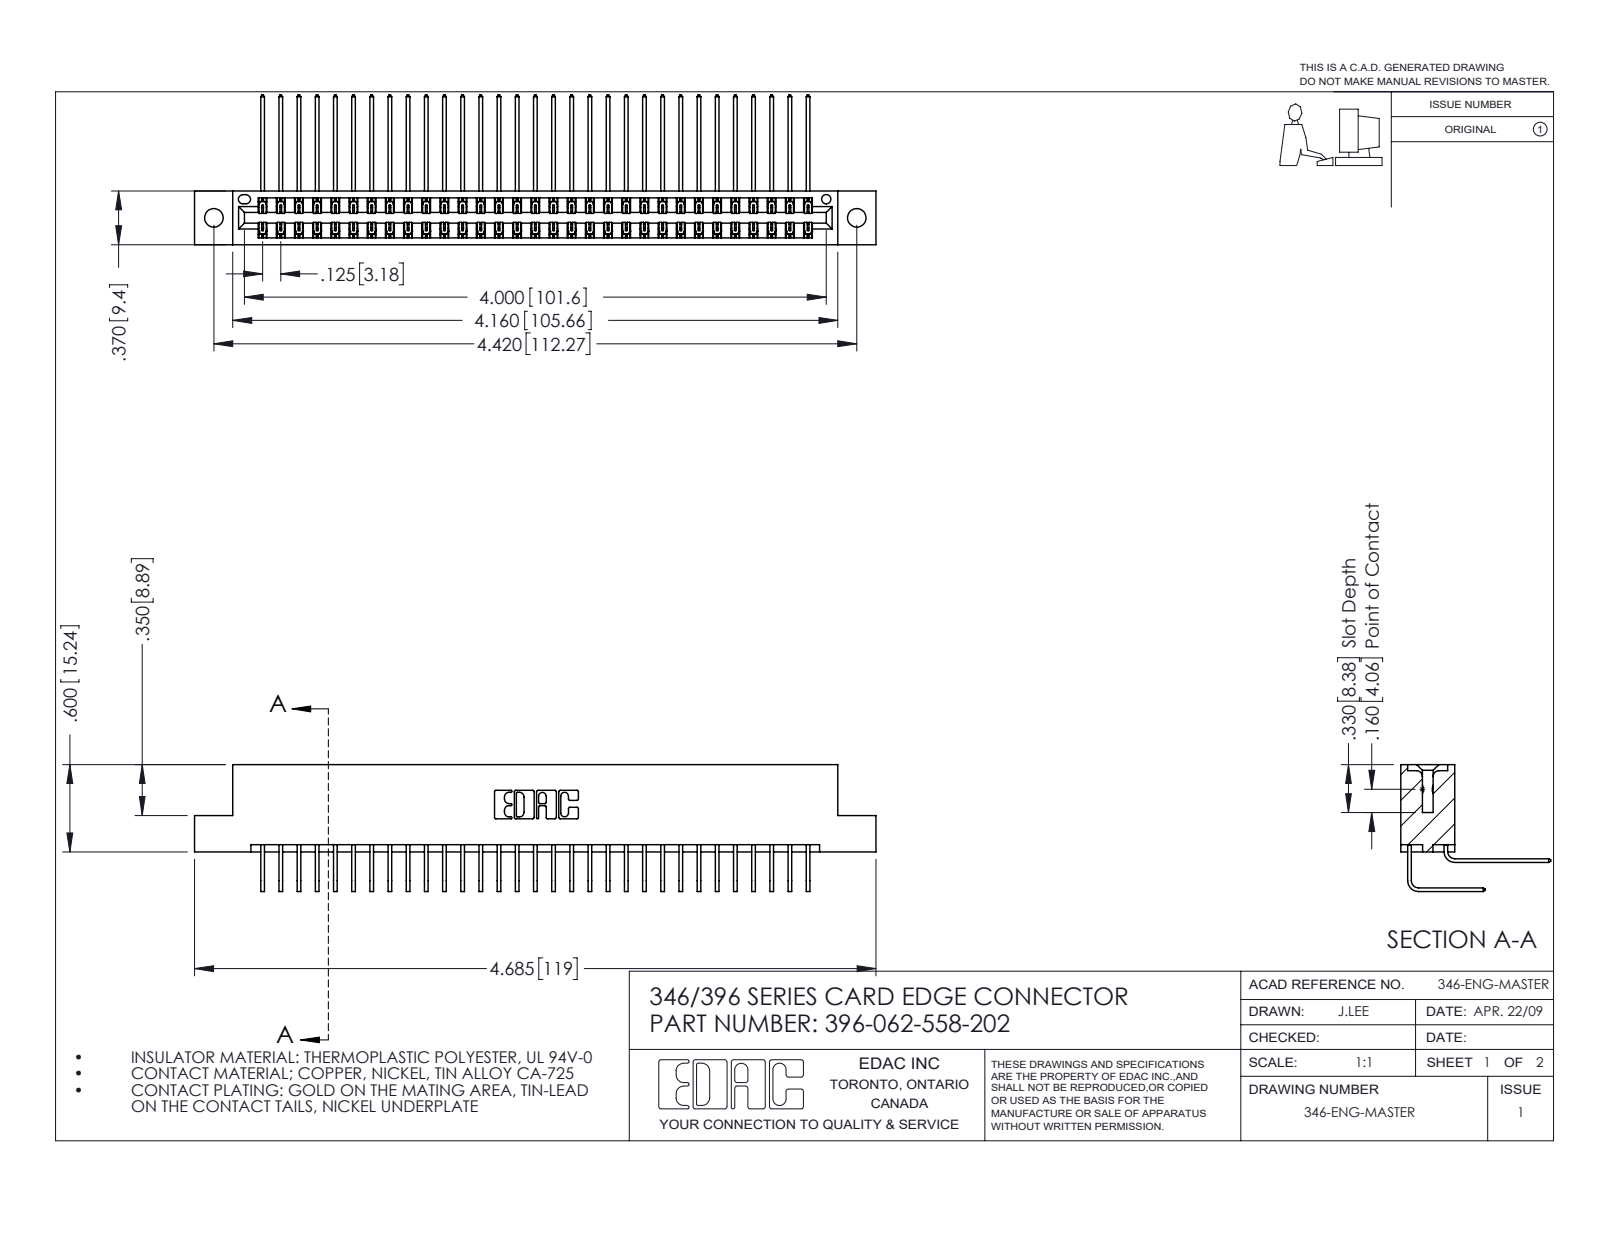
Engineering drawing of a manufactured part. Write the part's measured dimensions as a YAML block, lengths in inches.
part_name: "346 Part_Flush Mounting Lugs - 0.128 Dia; 345-292-001_558 559 Tail - 1; 396-062-558-202; 345-292-001_558 Tail - 2"
step_written_by: "SolidWorks 2016 (CONFIG_CONTROL_DESIGN)"
units: inches
bodies: {solids: 63, faces: 3470, planar: 2370, cylindrical: 1100, other: 0}
overall_size: [4.685, 1.03, 0.873]
volume: 0.722
surface_area: 27.2
round_holes:
  - {diameter: 0.128, count: 2}
  - {diameter: 0.064, count: 1}
partial_cylinders:
  - {radius: 0.006, count: 93}
  - {radius: 0.01, count: 22}
  - {radius: 0.007, count: 6}
  - {radius: 0.031, count: 6}
  - {radius: 0.026, count: 3}
  - {radius: 0.014, count: 2}
  - {radius: 0.022, count: 2}
  - {radius: 0.024, count: 2}
face_to_face_distances: [0.322, 0.048, 0.025, 0.25, 0.37, 0.298, 0.072, 0.275, 0.148, 0.222]
hole_center_spacings: [0.246, 4.212, 4.42]
